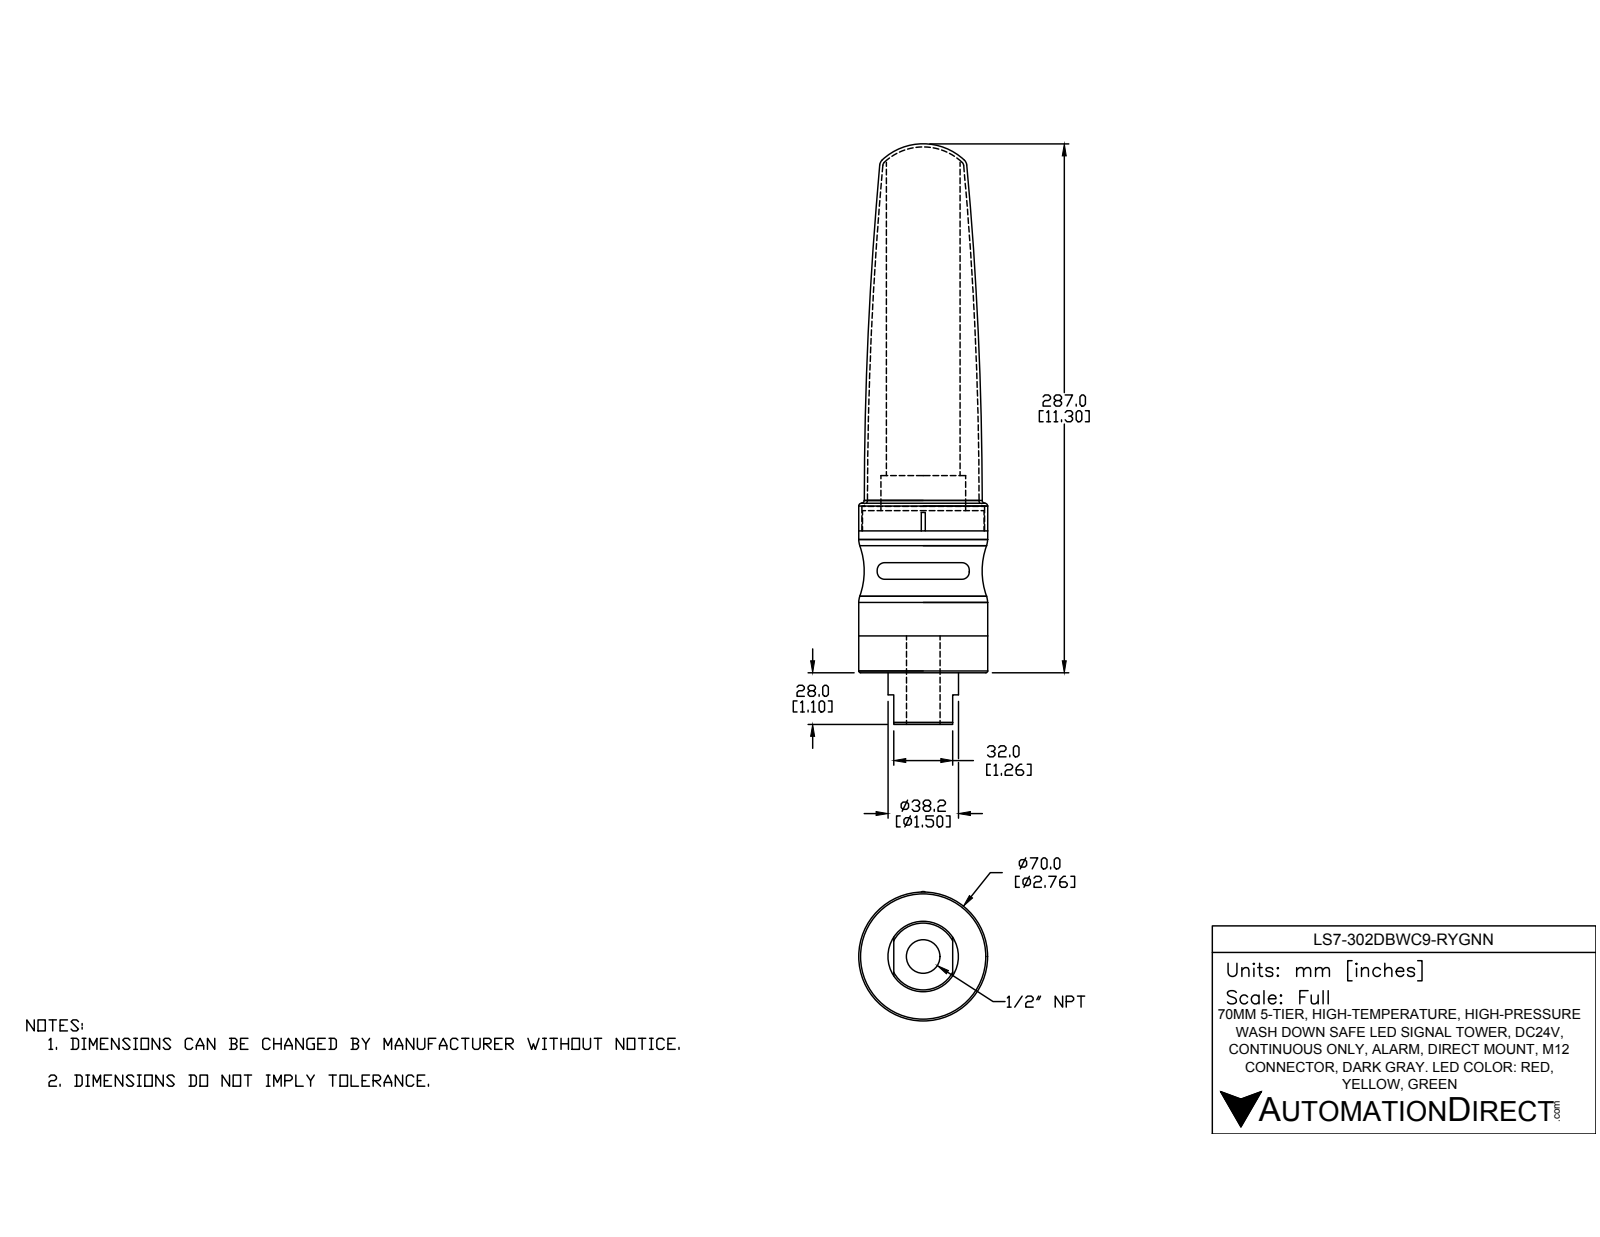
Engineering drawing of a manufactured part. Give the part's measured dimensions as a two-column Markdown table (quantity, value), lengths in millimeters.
| quantity | value |
| --- | --- |
| part name | LS7-302DBWC9-RYGNN |
| STEP written by | SolidWorks 2016 (AUTOMOTIVE_DESIGN) |
| units | millimeters |
| bodies | 4 solids, 60 faces (17 planar, 20 cylindrical, 23 other) |
| overall size | 275.5 × 70.3 × 70 |
| volume | 472 008 mm³ |
| surface area | 133 775 mm² |
| round holes (diameter × count) | 18.2 × 1, 66.6 × 1 |
| round bosses / shafts (diameter × count) | 70 × 1, 46 × 1, 40 × 1, 38 × 1 |
| partial cylindrical surfaces (radius × count) | 1 × 1, 2 × 1 |
| main face-to-face distances | 35.5, 19.5, 55, 37, 17.5, 18, 229.62, 210.12, 192.62, 174.62 |
